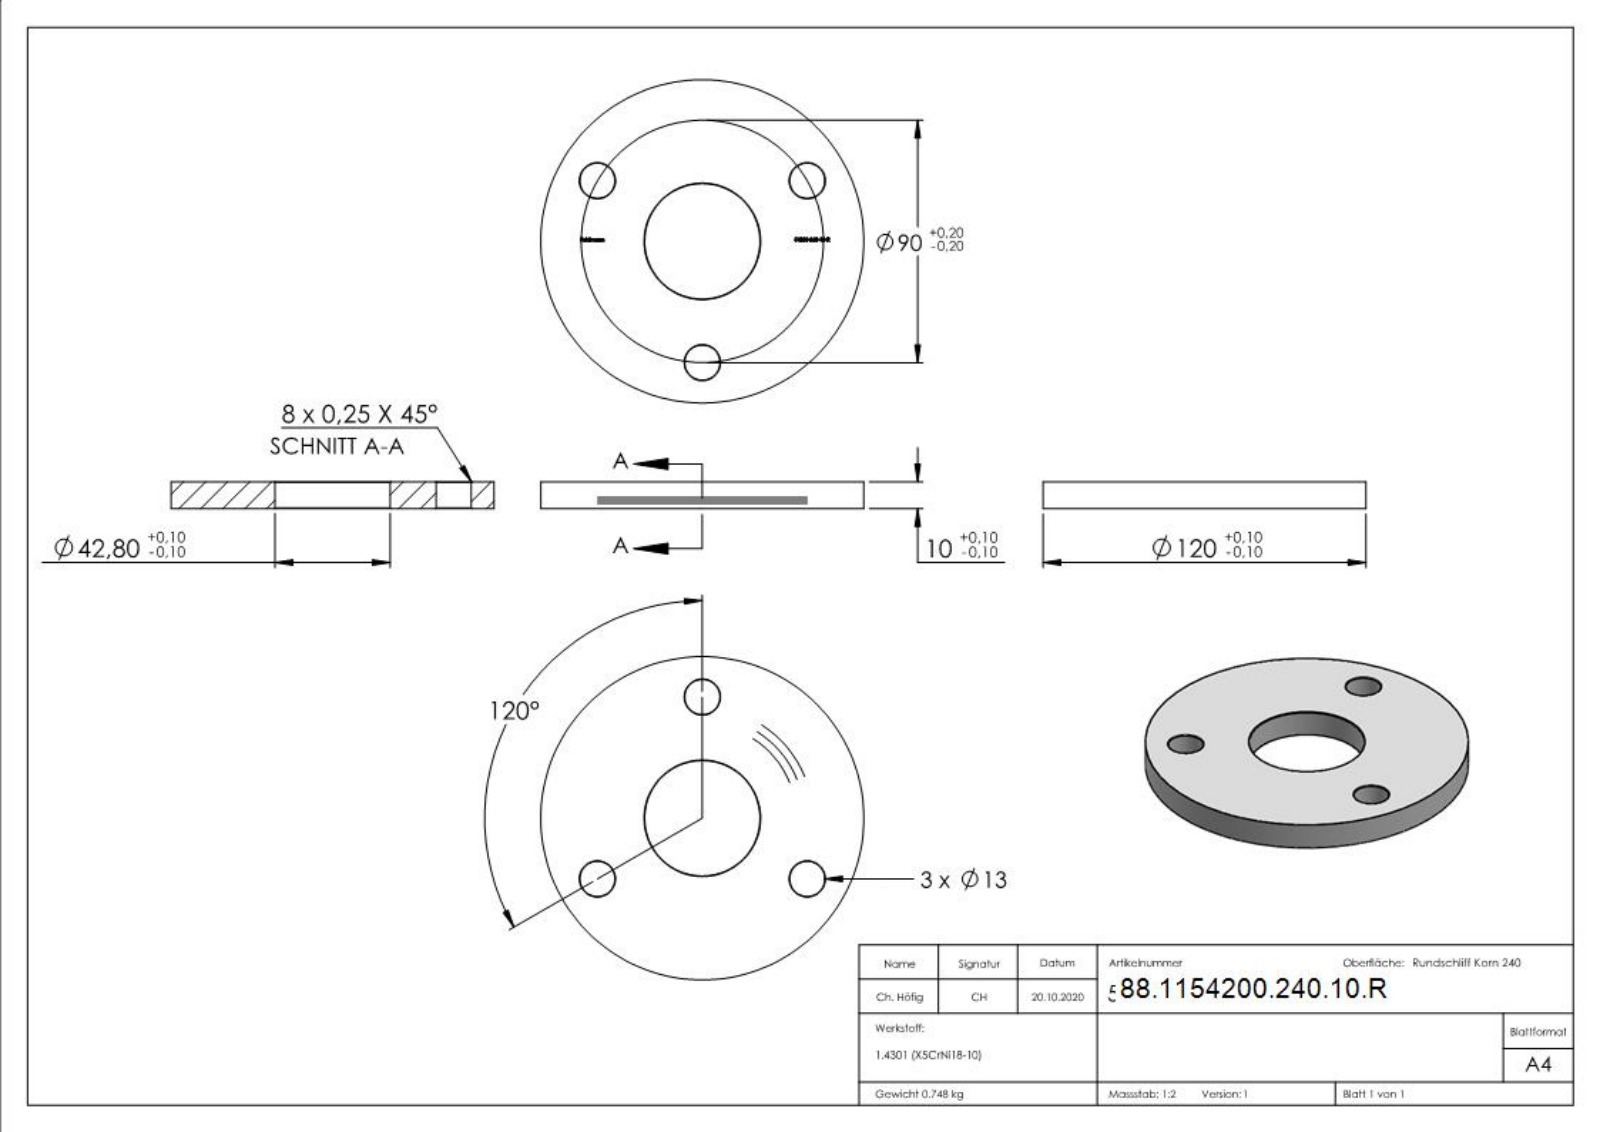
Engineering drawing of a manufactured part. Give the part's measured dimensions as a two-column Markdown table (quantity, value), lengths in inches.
| quantity | value |
| --- | --- |
| part name | 54200-240-10-R |
| STEP written by | SolidWorks 2018 (CONFIG_CONTROL_DESIGN) |
| units | inches |
| bodies | 1 solid, 296 faces (161 planar, 10 cylindrical, 125 other) |
| overall size | 4.724 × 4.724 × 0.394 |
| volume | 5.78 in³ |
| surface area | 39.1 in² |
| round holes (diameter × count) | 0.512 × 3, 1.685 × 1 |
| round bosses / shafts (diameter × count) | 4.724 × 1 |
| main face-to-face distances | 0.394, 0.39, 0.017, 0.035, 0.023, 3.432, 0.08, 3.604, 3.525, 3.511 |
| hole center spacings | 1.772, 3.069 |
